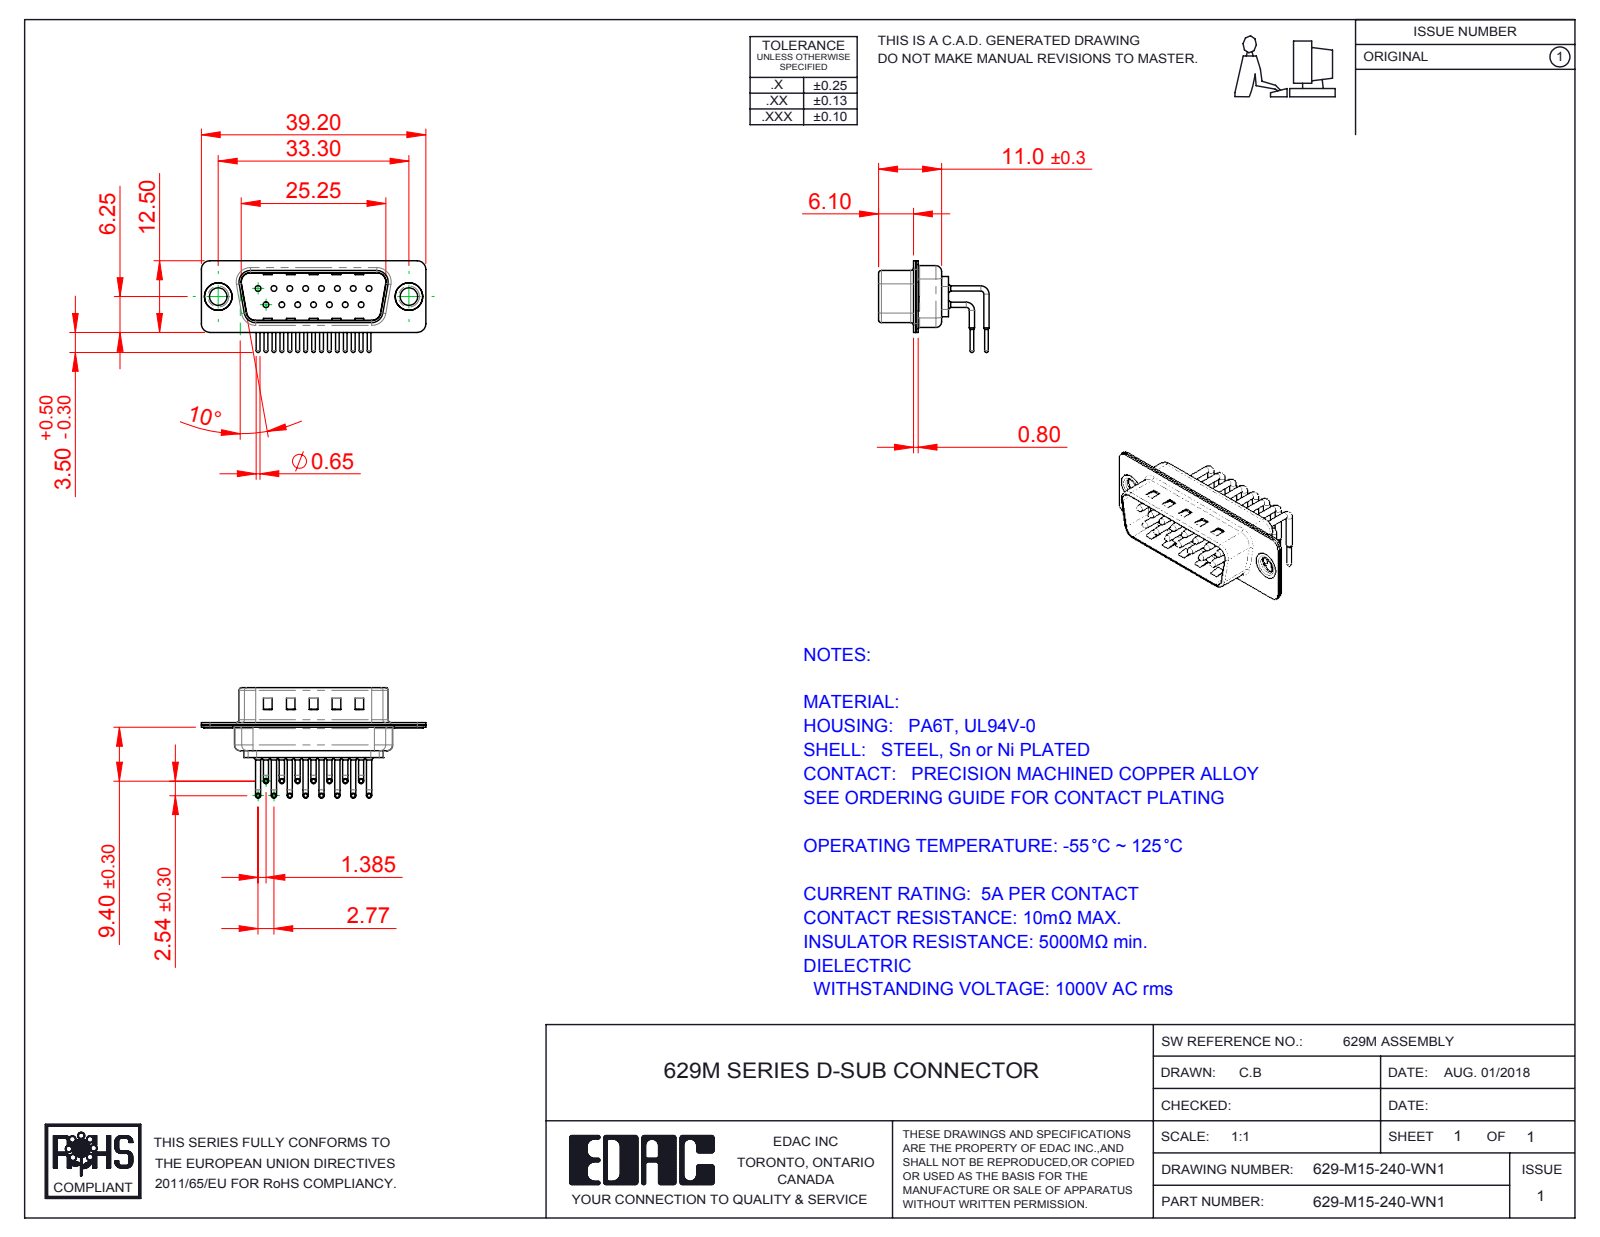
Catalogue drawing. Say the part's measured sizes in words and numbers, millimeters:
The part is named "629M Housing_15 Contacts; 629M Shell Rear_15 Contacts; 629M Contact Row 1; 629M Contact Row 2 (+3 more)". Its 3-D file was written by "SolidWorks 2016 (CONFIG_CONTROL_DESIGN)". It is 20 solids with 1964 faces: 1099 planar, 657 cylindrical and 208 other. Overall it measures 39.2 by 19.29 by 16 millimeters. Its volume is 1 881 cubic millimeters and its surface area 5 213 square millimeters. Round holes: 15 of diameter 1, 15 of diameter 1.7, 15 of diameter 2, 2 of diameter 3.05, 2 of diameter 4, 2 of diameter 4.8. Round bosses or shafts: 30 of diameter 0.9, 15 of diameter 1.5, 15 of diameter 0.65, 2 of diameter 5, 2 of diameter 4.9, 2 of diameter 3.55. Partial cylindrical surfaces (rounded edges, fillets, slot ends): 16 of radius 1.5, 15 of radius 1.01, 12 of radius 2, 8 of radius 0.5, 8 of radius 1.6, 4 of radius 0.25, 4 of radius 0.6, 4 of radius 0.65. The main face-to-face distances are 0.4, 0.85, 9.55, 8.7, 1.25, 0.8, 10.4, 1.5, 0.35, 1.9. The hole center spacings are 3.16, 2.77, 5.54, 8.31, 11.08, 5.03, 5.04, 7.48.
